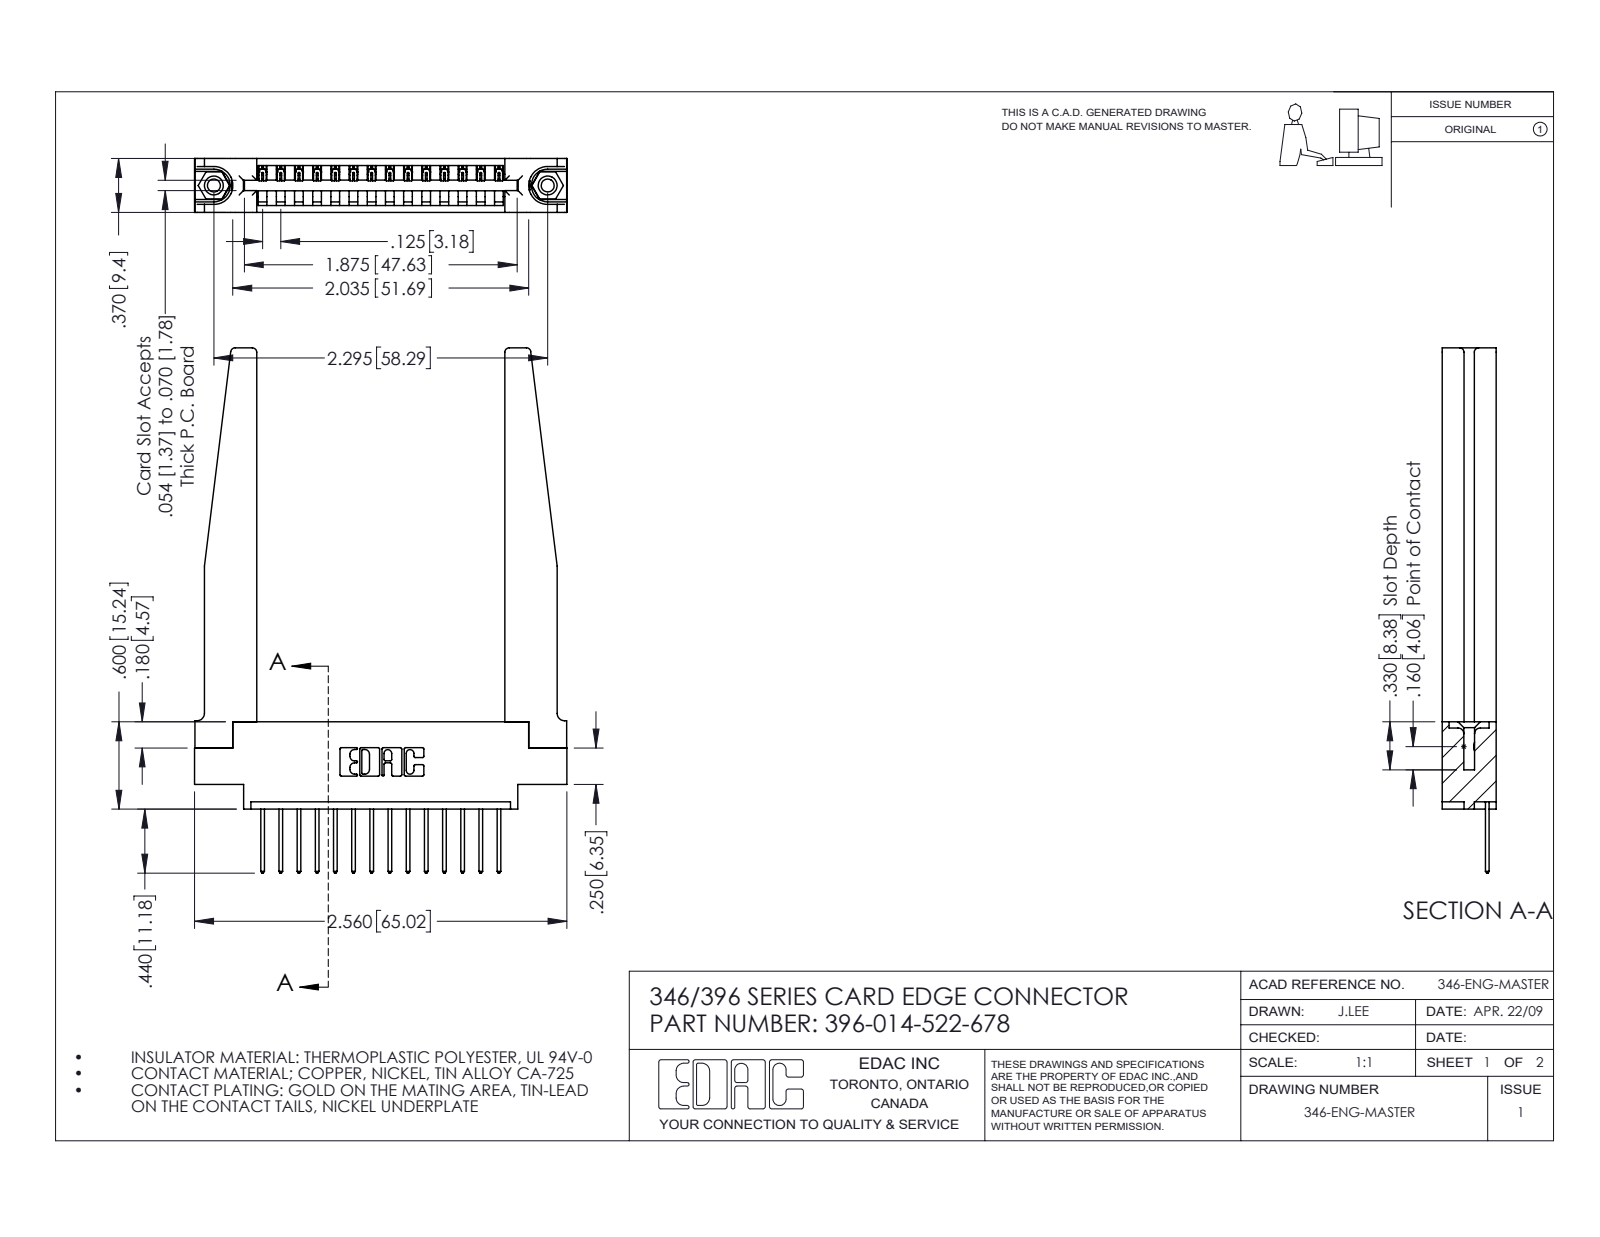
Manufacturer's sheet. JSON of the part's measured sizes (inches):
{"part_name": "345-292-001_345-293-122; 396-014-522-678; 346-220-078_345-220-078; 345-250-001_345-250-001-102 (+1 more)", "step_written_by": "SolidWorks 2016 (CONFIG_CONTROL_DESIGN)", "units": "inches", "bodies": {"solids": 19, "faces": 1172, "planar": 782, "cylindrical": 338, "other": 52}, "overall_size": [3.61, 2.56, 0.37], "volume_in3": 0.78, "surface_area_in2": 21.39, "round_holes": [[0.089, 2], [0.125, 2], [0.156, 2], [0.064, 1]], "round_bosses_or_shafts": [[0.155, 2]], "partial_cylinders_radius": [[0.006, 28], [0.01, 28], [0.01, 22], [0.03, 8], [0.007, 6], [0.031, 6], [0.026, 3], [0.031, 2]], "face_to_face_distances": [0.37, 0.15, 0.072, 0.148, 0.048, 0.322, 0.25, 0.102, 0.22, 0.173], "hole_center_spacings": [0.246, 2.089, 2.295]}
